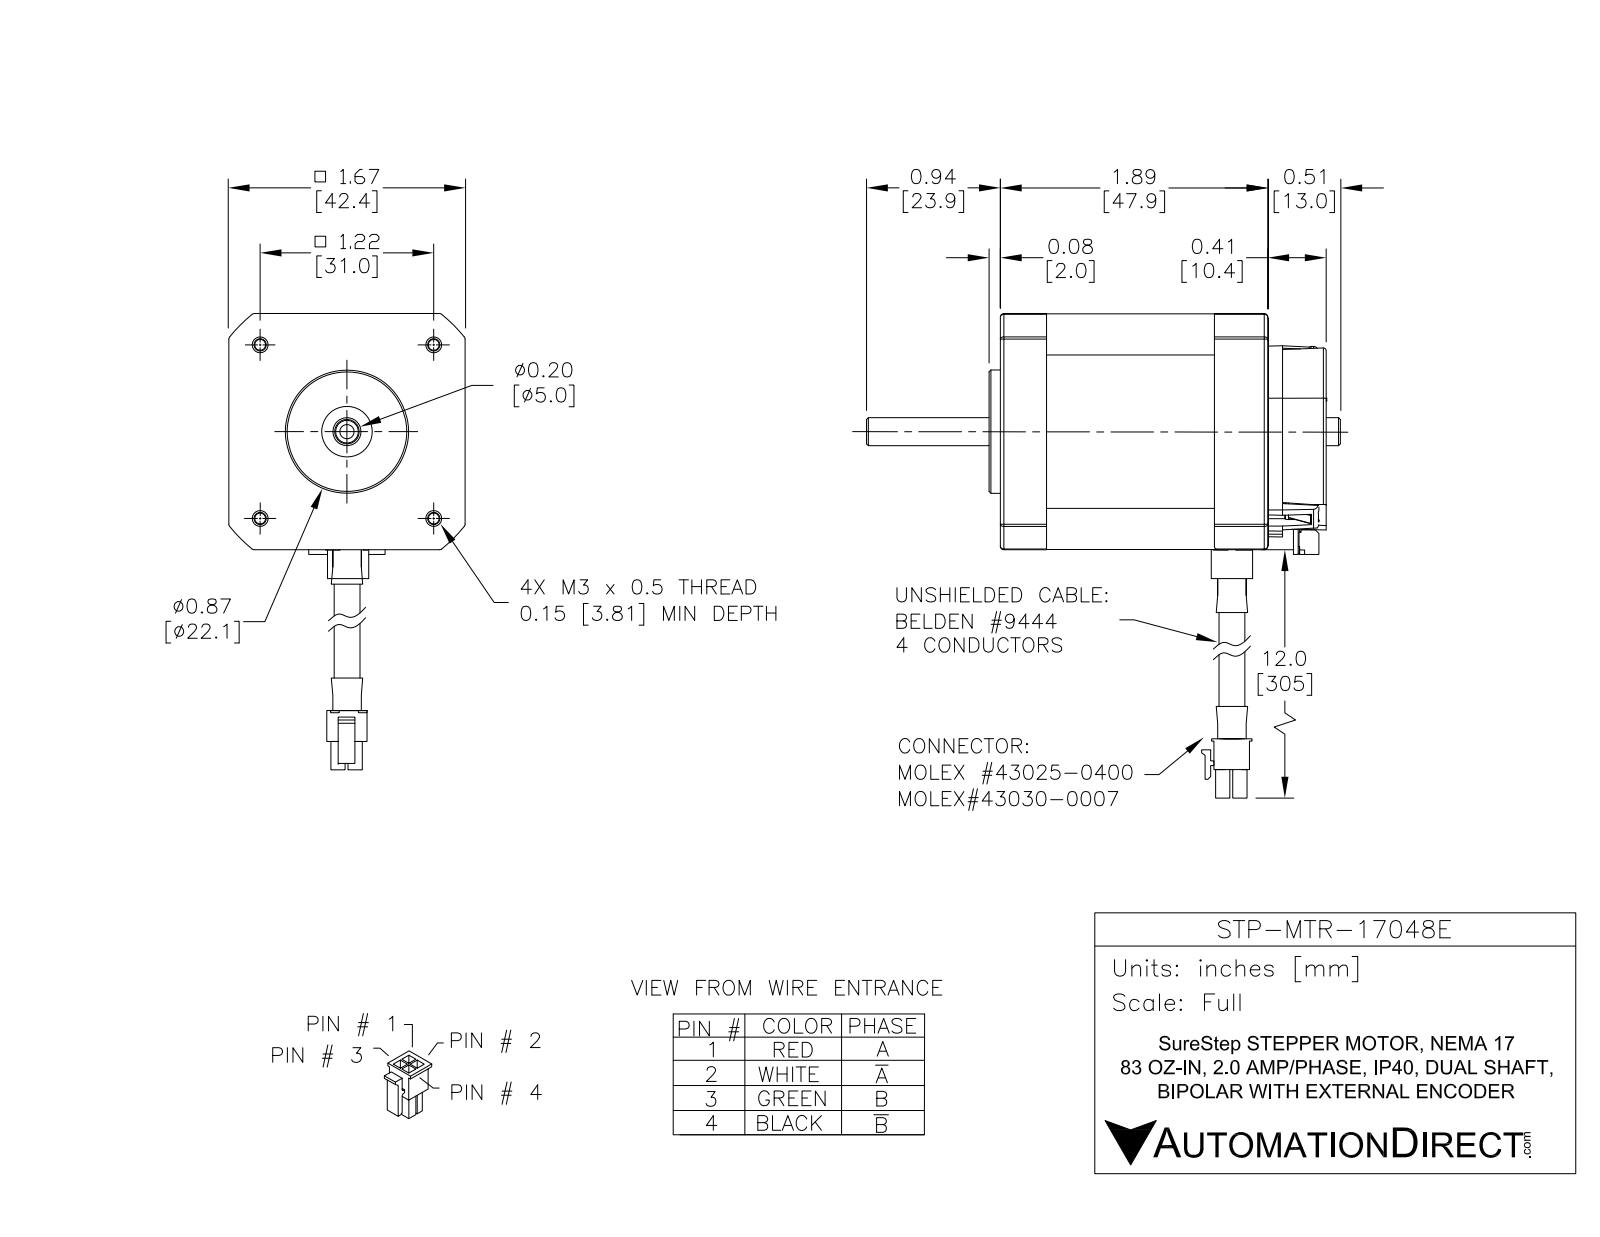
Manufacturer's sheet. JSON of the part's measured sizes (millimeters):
{"part_name": "STP-MTR-17048E", "step_written_by": "SolidWorks 2017 (AUTOMOTIVE_DESIGN)", "units": "millimeters", "bodies": {"solids": 15, "faces": 1642, "planar": 967, "cylindrical": 388, "other": 287}, "overall_size": [355, 84.6, 42.2], "volume_mm3": 95130, "surface_area_mm2": 29510, "round_holes": [[2, 6], [0.8, 4], [0.9, 4], [2.2, 4], [3.8, 4], [1.7, 2], [2.3, 2], [2.9, 2], [4.1, 2], [4.5, 2], [1.3, 1], [6.4, 1]], "round_bosses_or_shafts": [[3.3, 4], [1.5, 4], [22, 1], [11.8, 1], [10.5, 1], [7.4, 1], [5.5, 1], [5, 1]], "partial_cylinders_radius": [[1, 22], [0.6, 17], [0.5, 6], [1, 6], [2, 6], [0.3, 4], [0.4, 4], [2, 4]], "face_to_face_distances": [42.1, 42.1, 47.9, 42.2, 5.3, 53.2, 4.4, 2.5, 0.8, 52.3], "hole_center_spacings": [25.3, 9, 12.7, 18, 25.3, 29.4, 31, 9.2]}
